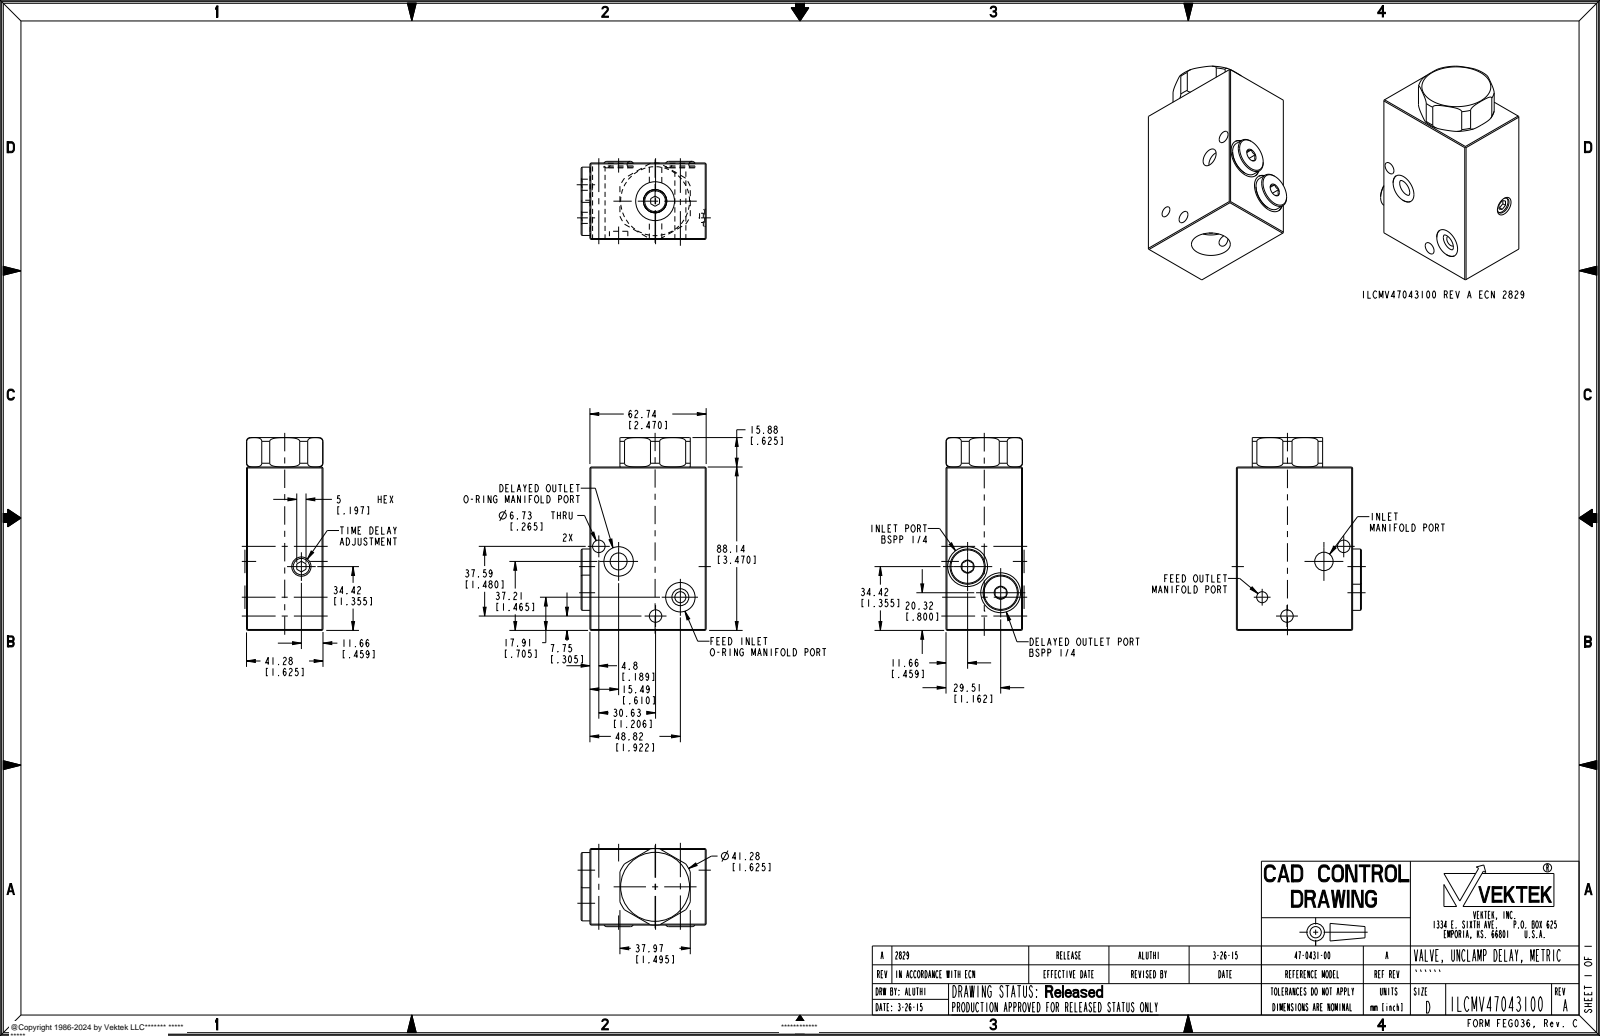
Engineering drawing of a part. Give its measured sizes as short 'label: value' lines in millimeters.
name: ILCMV47043100
written by: PRO/ENGINEER BY PARAMETRIC TECHNOLOGY CORPORATION, 2013320 (AUTOMOTIVE_DESIGN)
unit: mm
bodies: 1 solid, 131 faces (63 planar, 36 cylindrical, 32 other)
size: 104.01 × 67.48 × 42.14
volume: 241 273 mm³; area: 30 226 mm²
holes: 2× ⌀6.73, 2× ⌀15.88, 2× ⌀21.49, 1× ⌀5.94, 1× ⌀8.84, 1× ⌀9.93, 1× ⌀20.95
bosses: 2× ⌀19
rounds: 1× R20.64
face distances: 41.27, 62.74, 88.14, 104.02, 15.88, 37.97, 4.75, 67.49, 38.61, 2.66
hole spacings: 13.43, 16.81, 22.75, 35.57, 38.51, 48.49, 51.87
